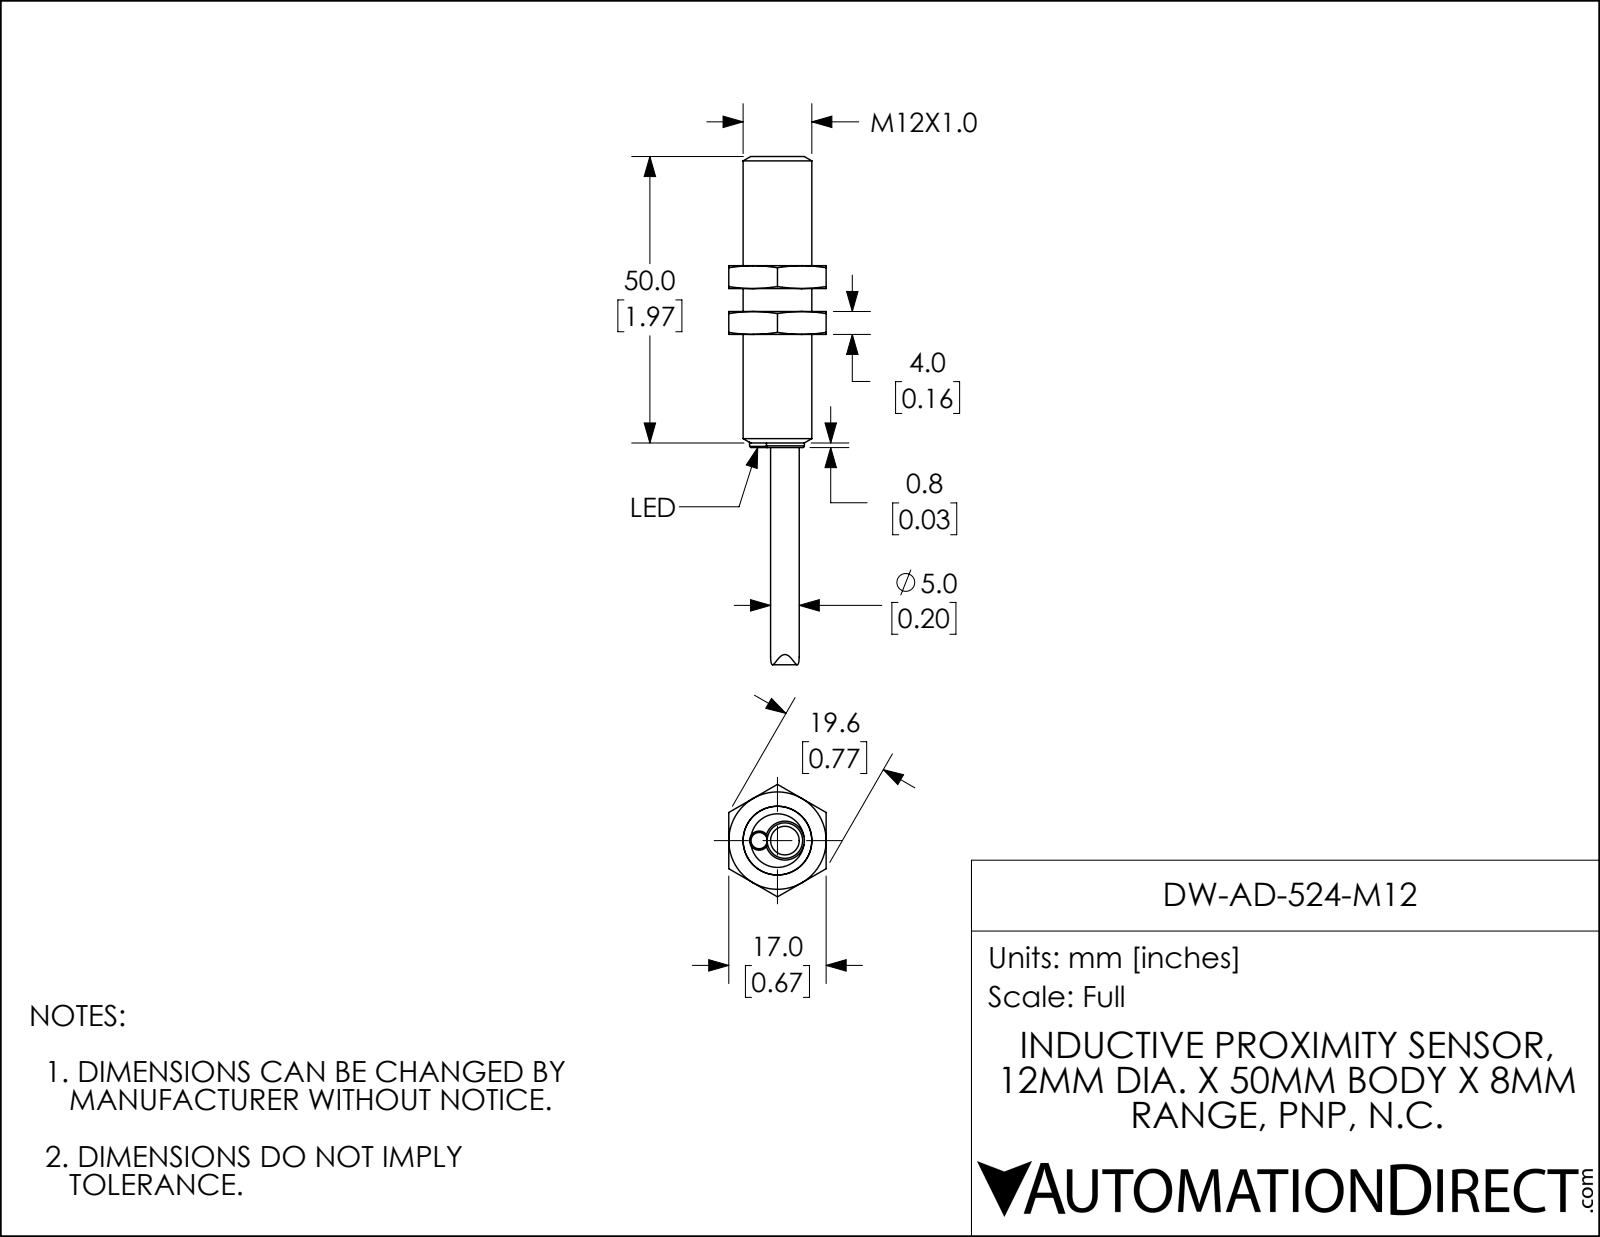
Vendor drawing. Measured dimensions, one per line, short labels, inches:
name: DW-AD-521-M12
written by: SolidWorks 2017 (AUTOMOTIVE_DESIGN)
unit: in
bodies: 1 solid, 14 faces (5 planar, 4 cylindrical, 5 other)
size: 3.492 × 0.472 × 0.472
volume: 0.389 in³; area: 4.131 in²
bosses: 1× ⌀0.472, 1× ⌀0.268, 1× ⌀0.197
rounds: 1× R0.066
face distances: 1.969, 2, 0.031
